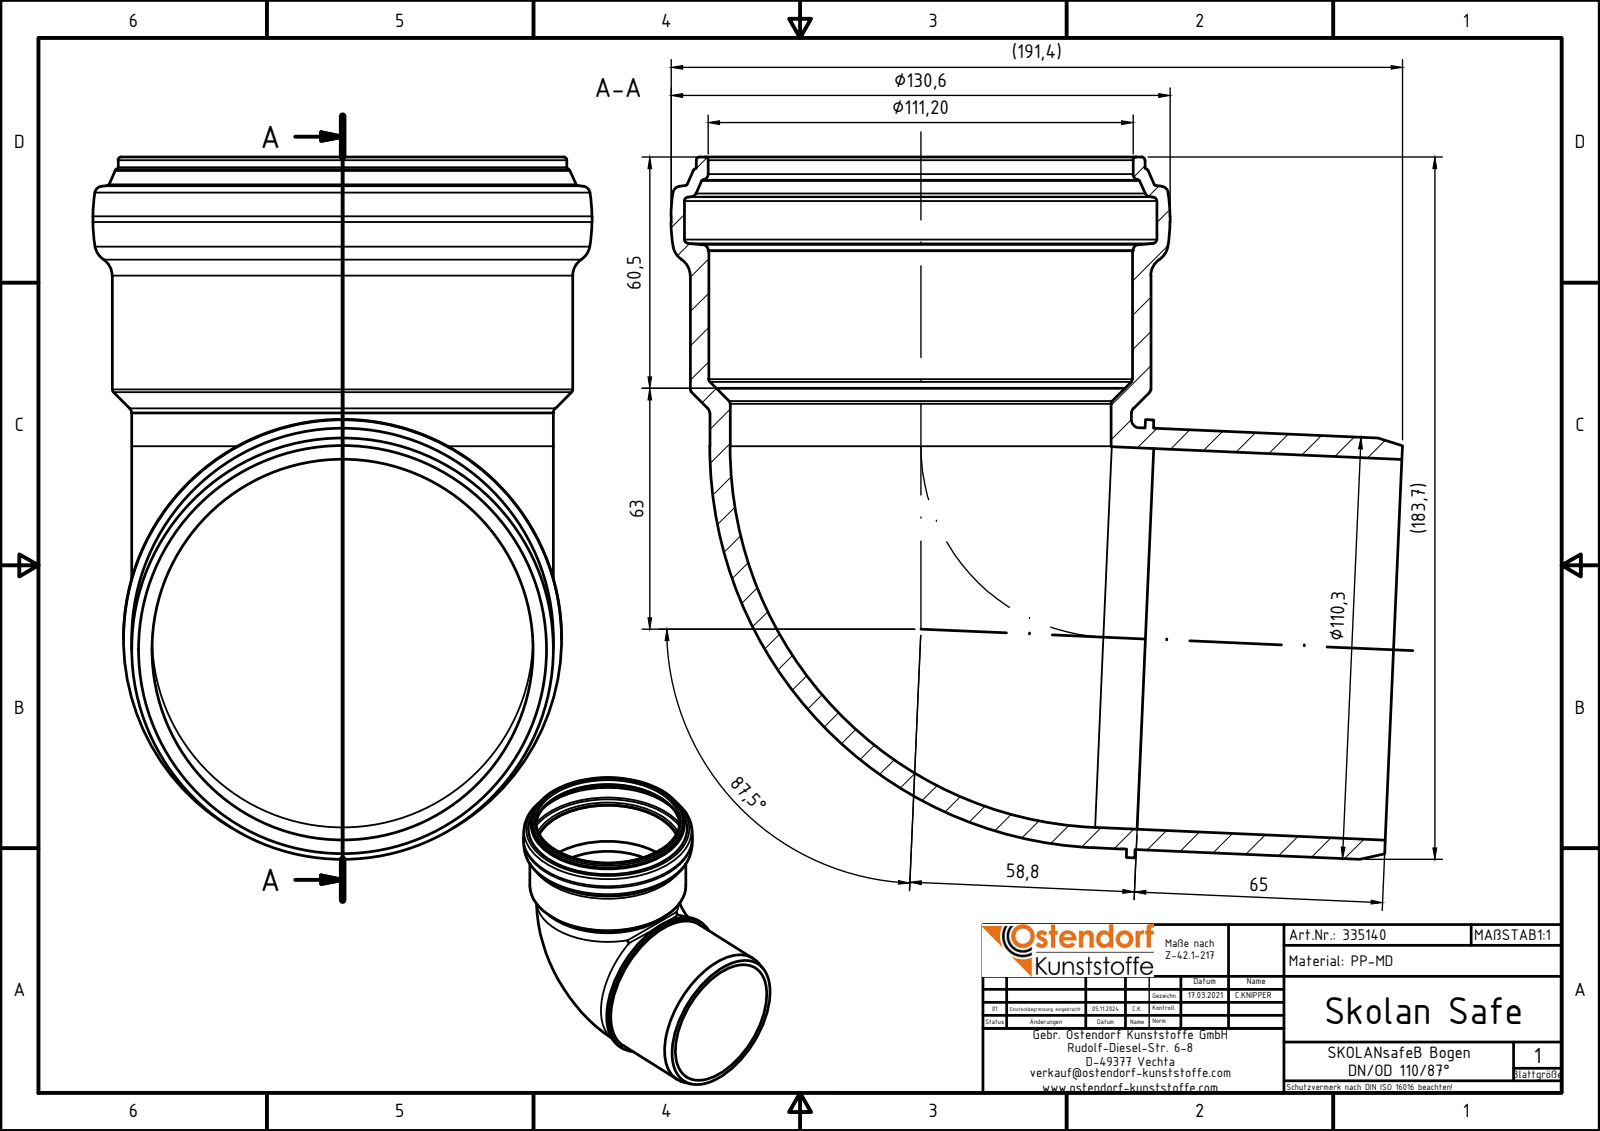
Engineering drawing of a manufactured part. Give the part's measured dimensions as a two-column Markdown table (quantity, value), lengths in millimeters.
| quantity | value |
| --- | --- |
| part name | 335140z |
| STEP written by | Autodesk Inventor 2024 (AUTOMOTIVE_DESIGN) |
| units | millimeters |
| bodies | 1 solid, 50 faces (5 planar, 14 cylindrical, 31 other) |
| overall size | 191.38 × 183.72 × 130.6 |
| volume | 400 882 mm³ |
| surface area | 165 387 mm² |
| round holes (diameter × count) | 99.7 × 2, 110.9 × 1, 111.2 × 1, 123.6 × 1 |
| round bosses / shafts (diameter × count) | 110.31 × 2, 130.6 × 1, 120.5 × 1, 117.4 × 1, 114.7 × 1, 110.3 × 1 |
| main face-to-face distances | 2.21, 67.5, 65.29, 24.5 |
